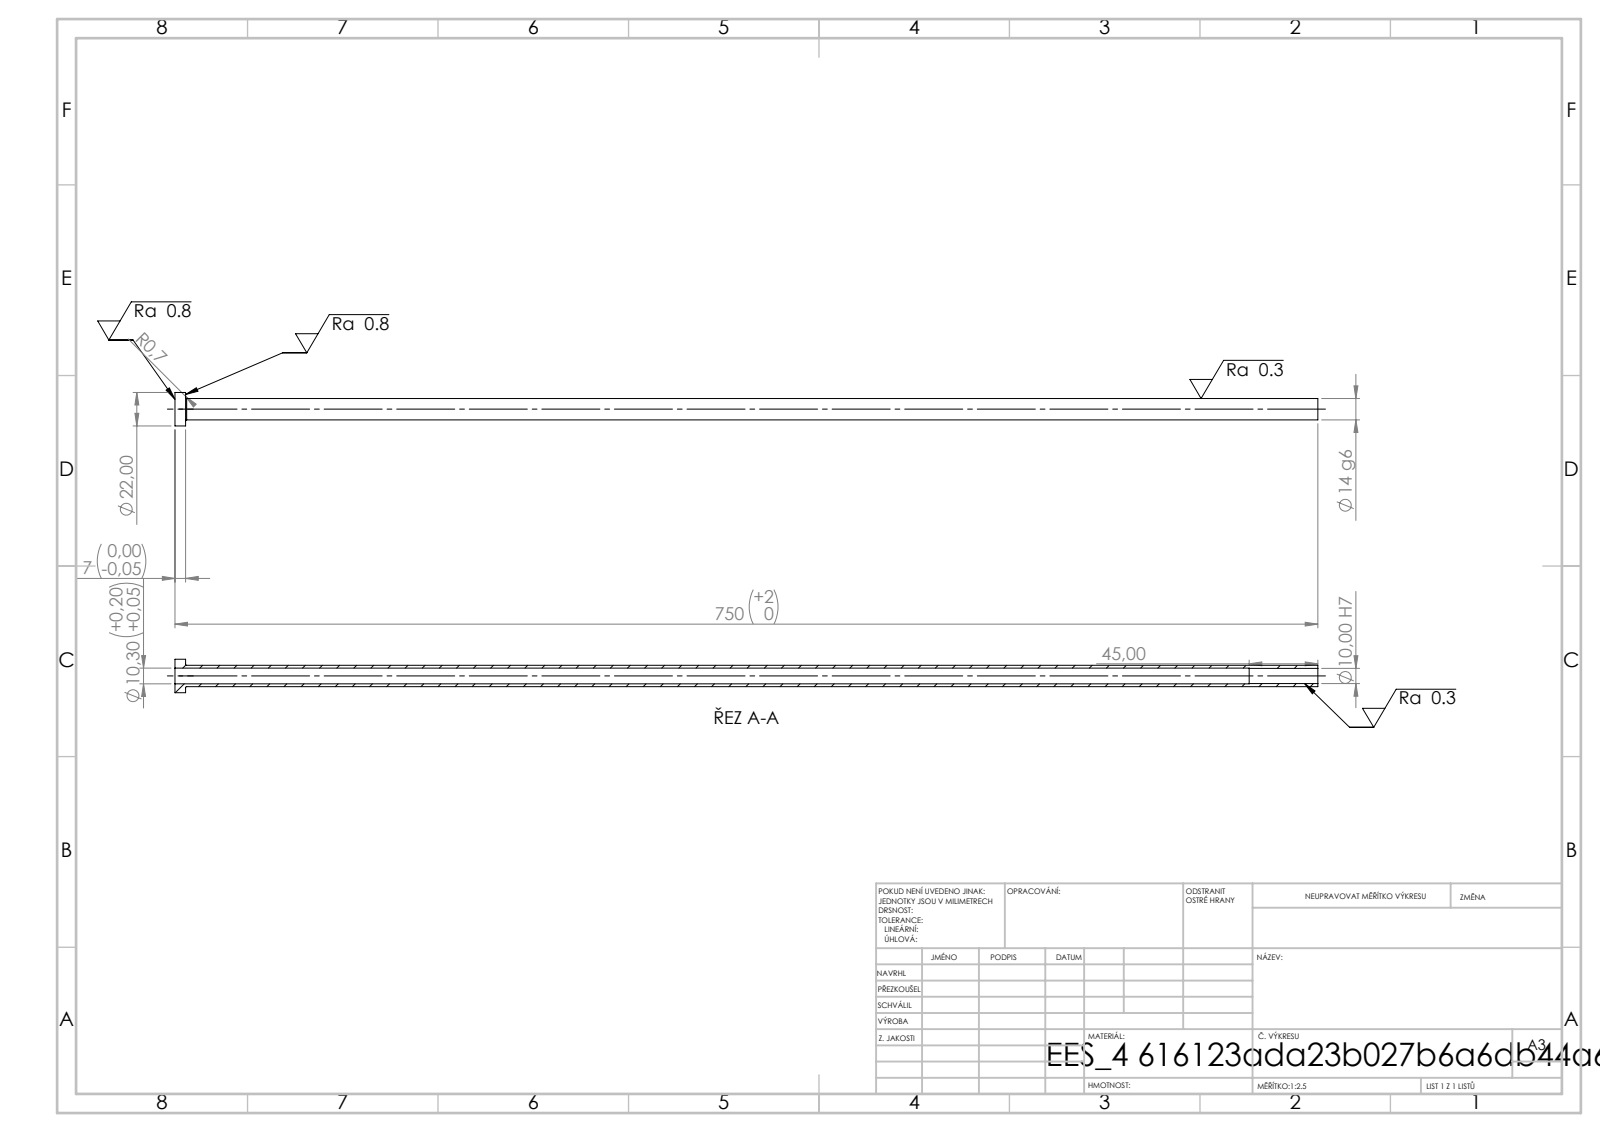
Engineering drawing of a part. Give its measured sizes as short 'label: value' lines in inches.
written by: SolidWorks 2019 (CONFIG_CONTROL_DESIGN)
unit: in
bodies: 1 solid, 14 faces (4 planar, 8 cylindrical, 2 other)
size: 29.528 × 0.866 × 0.866
volume: 3.342 in³; area: 89.87 in²
holes: 1× ⌀0.394, 1× ⌀0.406
bosses: 1× ⌀0.866, 1× ⌀0.551
face distances: 0.276, 29.528, 29.252, 27.756, 27.48, 1.772
